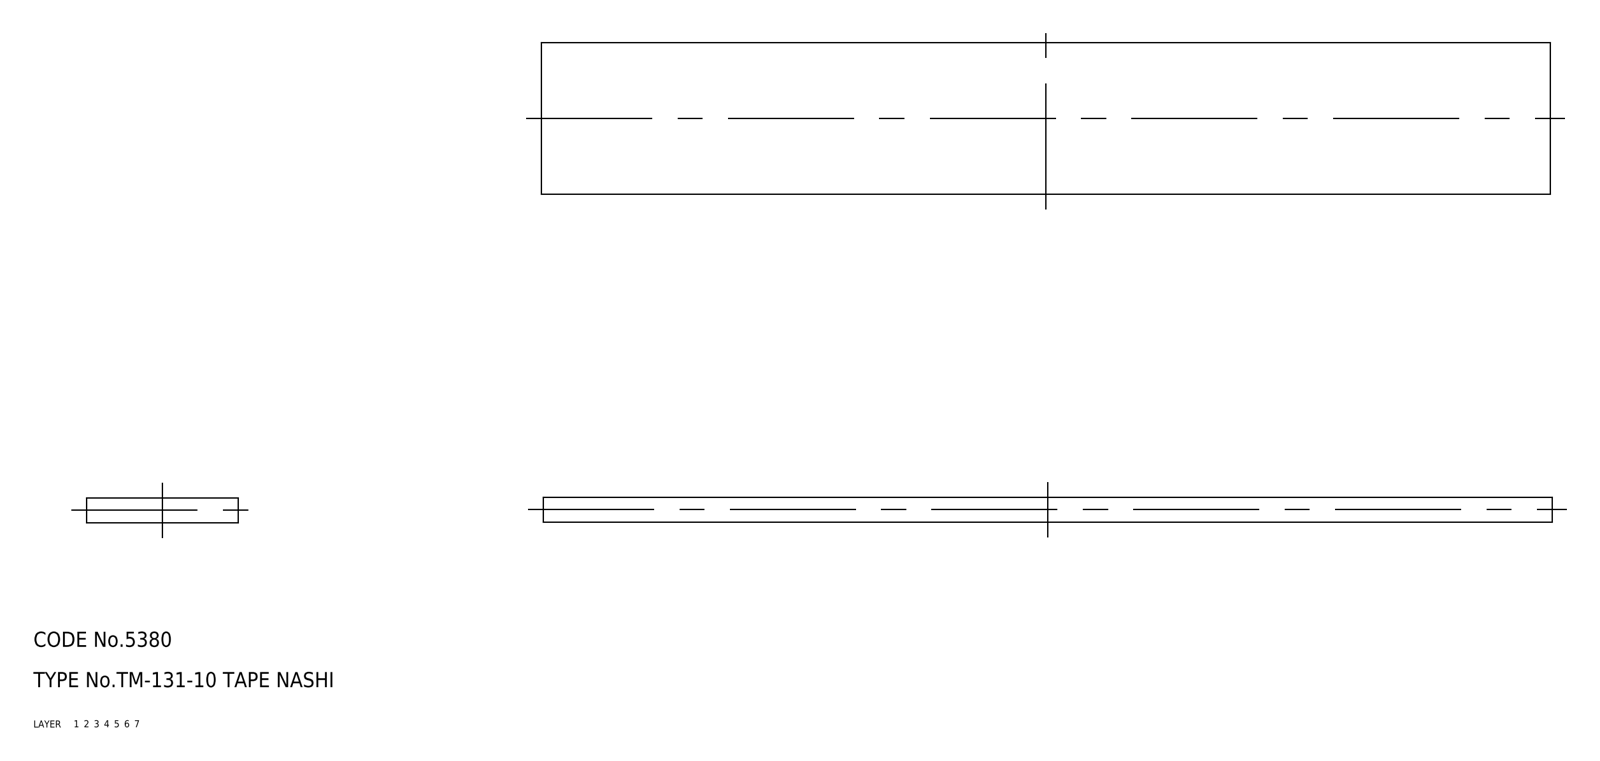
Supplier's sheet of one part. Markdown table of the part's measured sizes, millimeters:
| quantity | value |
| --- | --- |
| part name | rubber foam |
| STEP written by | CADfix (AUTOMOTIVE_DESIGN) |
| units | millimeters |
| bodies | 1 solid, 6 faces (0 planar, 0 cylindrical, 6 other) |
| overall size | 200 × 30 × 5 |
| volume | 30 000 mm³ |
| surface area | 14 300 mm² |
